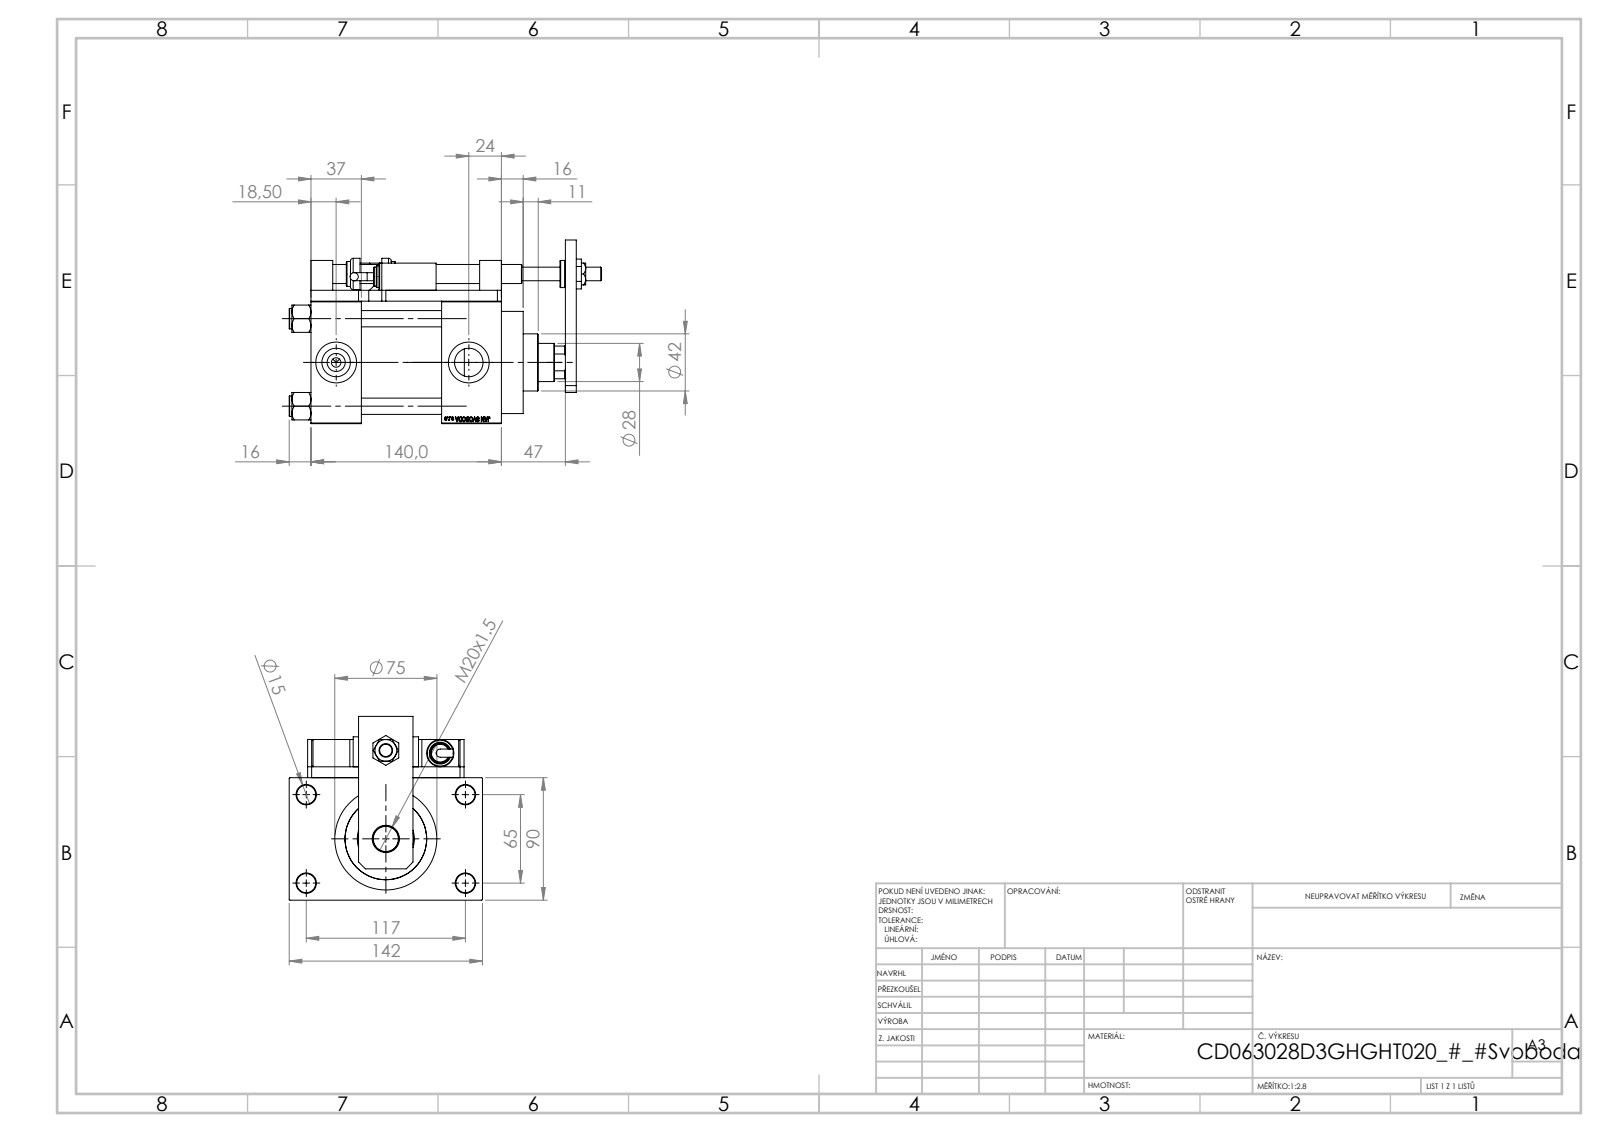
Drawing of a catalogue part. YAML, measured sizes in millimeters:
part_name: "V215CD_SWITCH_Q_TYC; V215CD_SWITCH_Q_DIMA; V215CD_SWITCH_Q_PODLOZKA_BACK; Zatka_pro_OIL_PORT (+7 more)"
step_written_by: "SolidWorks 2019 (CONFIG_CONTROL_DESIGN)"
units: millimeters
bodies: {solids: 26, faces: 1432, planar: 666, cylindrical: 167, other: 599}
overall_size: [229.5, 142, 135]
volume: 1356000
surface_area: 290182
round_holes:
  - {diameter: 14, count: 5}
  - {diameter: 8.5, count: 4}
  - {diameter: 12, count: 4}
  - {diameter: 13.5, count: 4}
  - {diameter: 20.96, count: 4}
  - {diameter: 30, count: 4}
  - {diameter: 7, count: 3}
  - {diameter: 10, count: 1}
  - {diameter: 18.5, count: 1}
  - {diameter: 20, count: 1}
  - {diameter: 28, count: 1}
  - {diameter: 31, count: 1}
round_bosses_or_shafts:
  - {diameter: 15, count: 4}
  - {diameter: 20, count: 3}
  - {diameter: 16, count: 2}
  - {diameter: 14, count: 2}
  - {diameter: 6, count: 2}
  - {diameter: 75, count: 1}
  - {diameter: 69, count: 1}
  - {diameter: 42, count: 1}
partial_cylinders:
  - {radius: 7.5, count: 4}
  - {radius: 13.5, count: 1}
face_to_face_distances: [8, 90, 44, 140, 37, 103, 98, 59, 96, 16]
hole_center_spacings: [66.92, 26.35, 45.47, 64.3, 69.81, 90.65, 111.34, 65]
